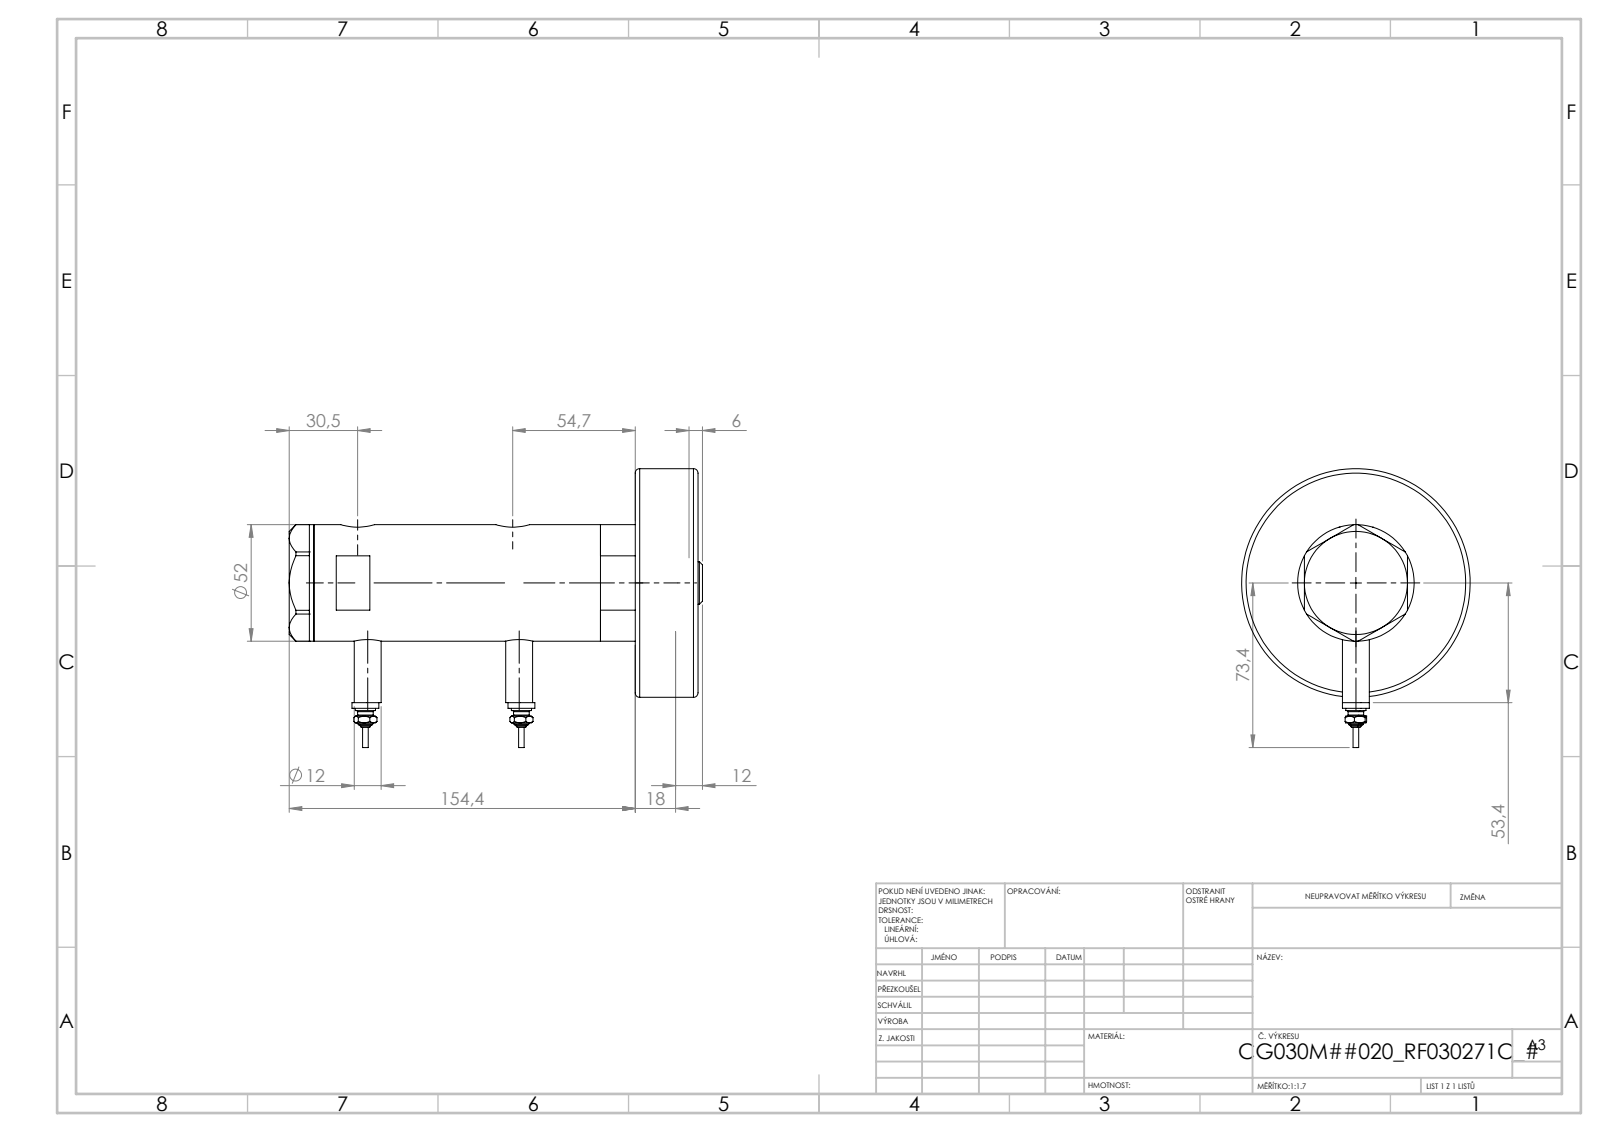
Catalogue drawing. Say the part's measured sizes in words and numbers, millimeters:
The part is named "V270CG_271C; V270CG_BACK; Switch; V270CG_FRONT (+2 more)". Its 3-D file was written by "SolidWorks 2019 (CONFIG_CONTROL_DESIGN)". It is 7 solids with 236 faces: 95 planar, 73 cylindrical and 68 other. Overall it measures 184.4 by 124.4 by 102 millimeters. Its volume is 537 926 cubic millimeters and its surface area 105 994 square millimeters. Round holes: 2 of diameter 9.73, 2 of diameter 12.5, 2 of diameter 15, 1 of diameter 6.5, 1 of diameter 20, 1 of diameter 21.5, 1 of diameter 30, 1 of diameter 33, 1 of diameter 40, 1 of diameter 44. Round bosses or shafts: 4 of diameter 12, 2 of diameter 9, 2 of diameter 7, 2 of diameter 4.5, 2 of diameter 2.5, 1 of diameter 102, 1 of diameter 52, 1 of diameter 38. The main face-to-face distances are 28, 143.4, 171.4, 91.5, 51.9, 79.9, 23.8, 67.7, 119.6, 147.6. The hole center spacings are 2.9, 4.5, 64.7, 67.6, 69.2, 72.1.
